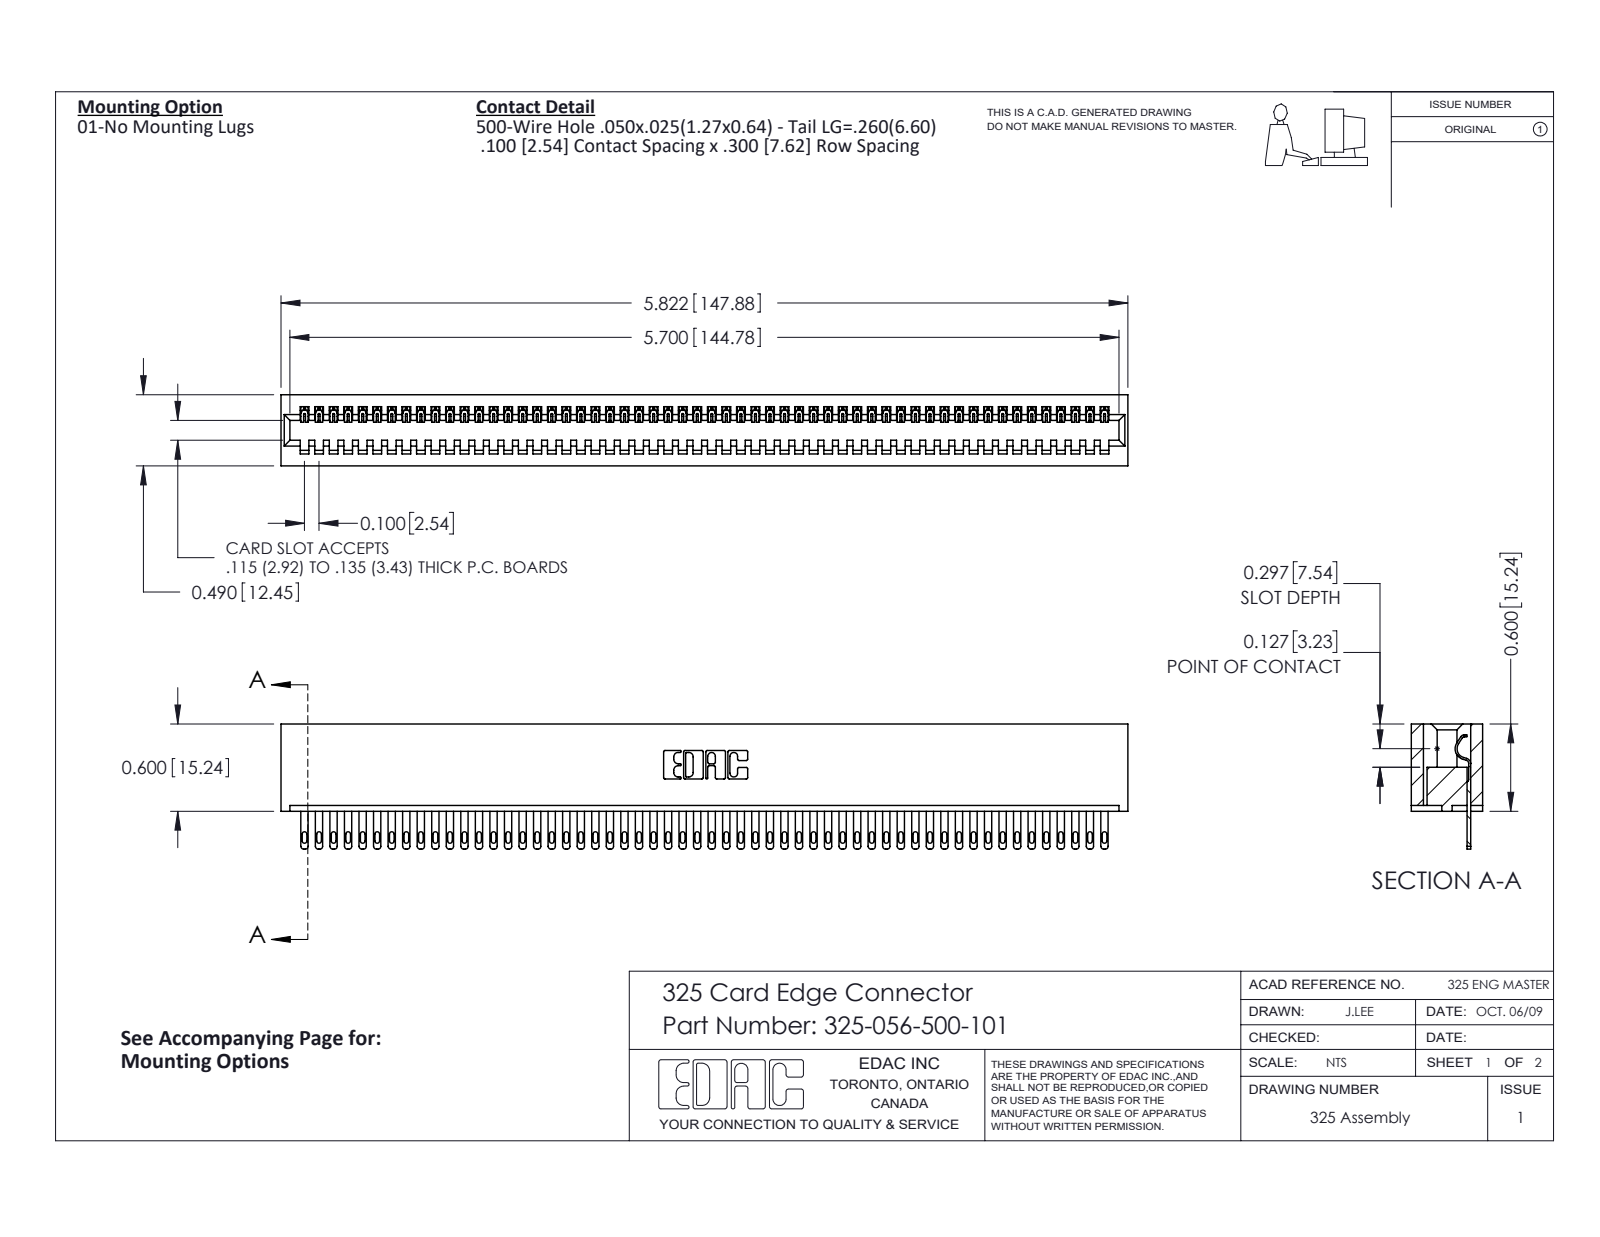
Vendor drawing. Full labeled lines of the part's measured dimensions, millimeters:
Part name (STEP PRODUCT): 325 Part_Lugless; 325-056-500-101; 325-292-001_325-293-100
STEP written by: SolidWorks 2016 (CONFIG_CONTROL_DESIGN)
Units: millimetres
Bodies: 57 solids, 3130 faces (2082 planar, 1048 cylindrical, 0 other)
Overall size (bounding box): 147.9 × 21.8 × 12.4
Volume: 19 480 mm³ · Surface area: 22 150 mm²
Partial cylindrical surfaces — rounded edges, fillets, slot ends (radius × count): R0.2 ×112, R0.4 ×112, R0.5 ×112, R0.3 ×22, R0.2 ×6, R0.8 ×6, R0.7 ×3, R0.4 ×1
Main face-to-face distances: 2.1, 10.3, 12.4, 7.6, 2.7, 9.7, 0.6, 8.3, 6.7, 14.2
